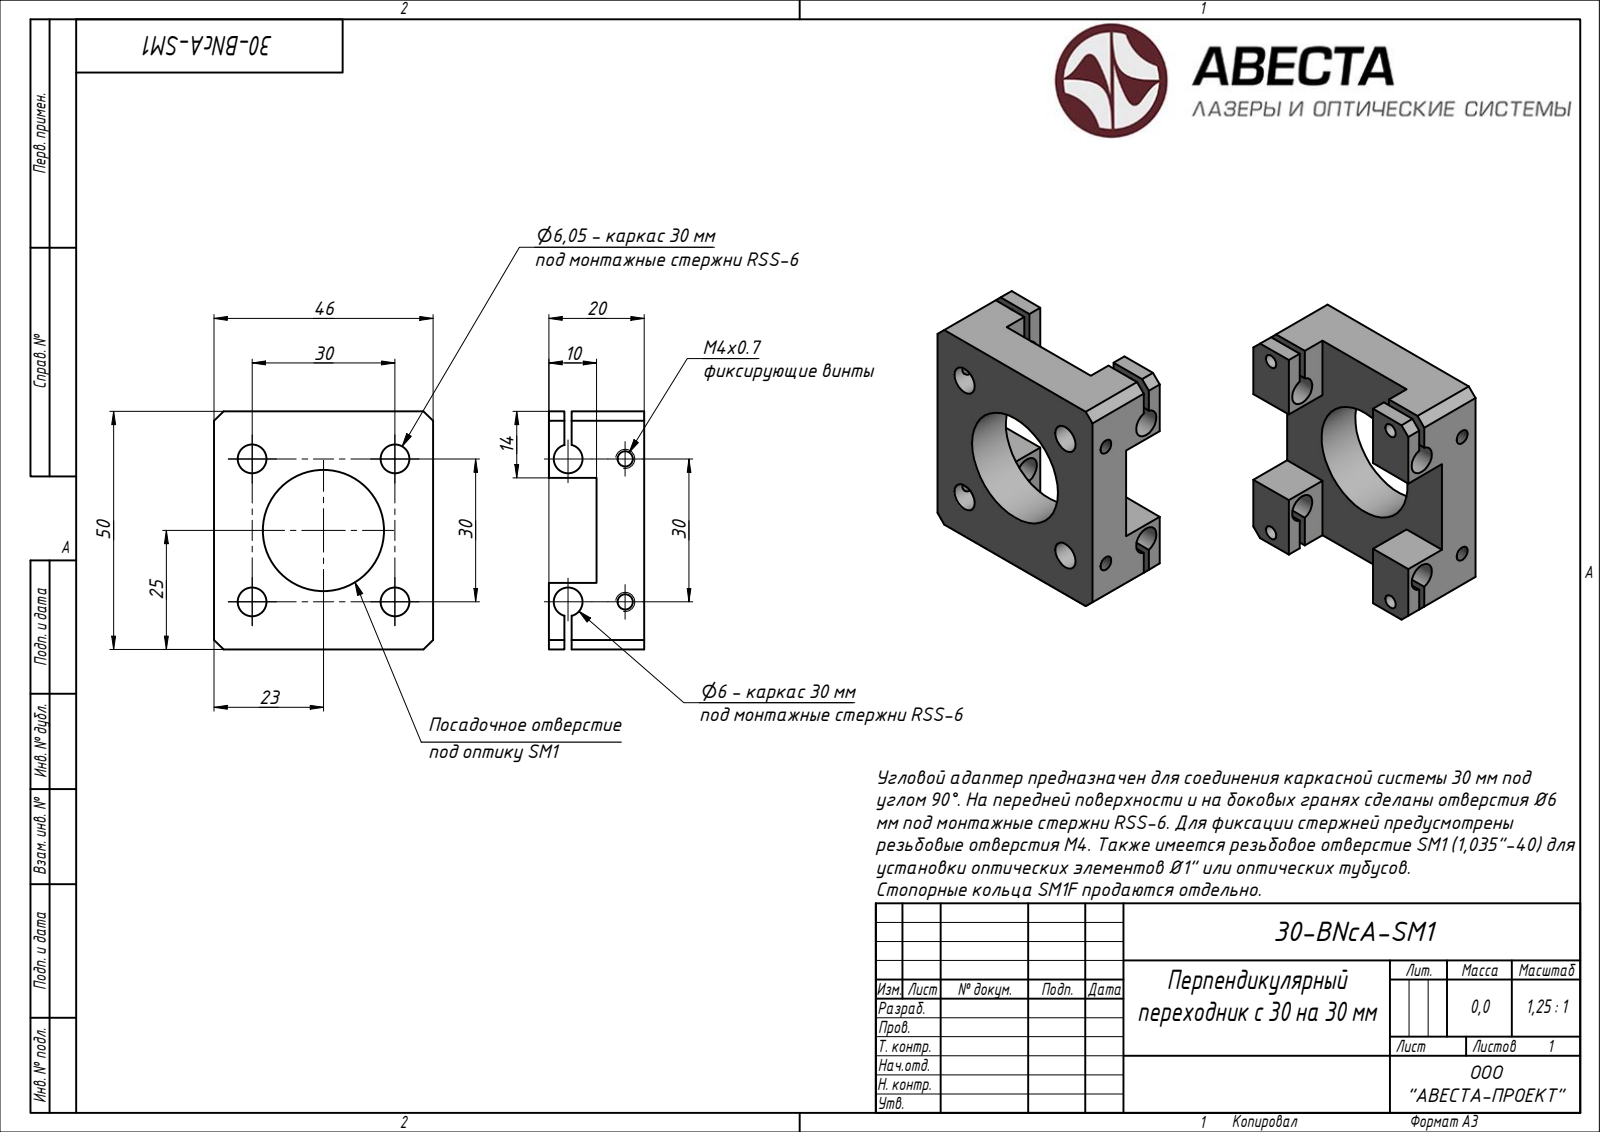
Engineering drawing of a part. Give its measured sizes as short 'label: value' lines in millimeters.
written by: ST-DEVELOPER v15 (AUTOMOTIVE_DESIGN)
unit: mm
bodies: 1 solid, 88 faces (42 planar, 0 cylindrical, 46 other)
size: 50 × 46 × 20
volume: 20 697 mm³; area: 10 100 mm²
face distances: 10, 46, 50, 20, 14, 36, 10.5, 35.5, 15.25, 5.25
